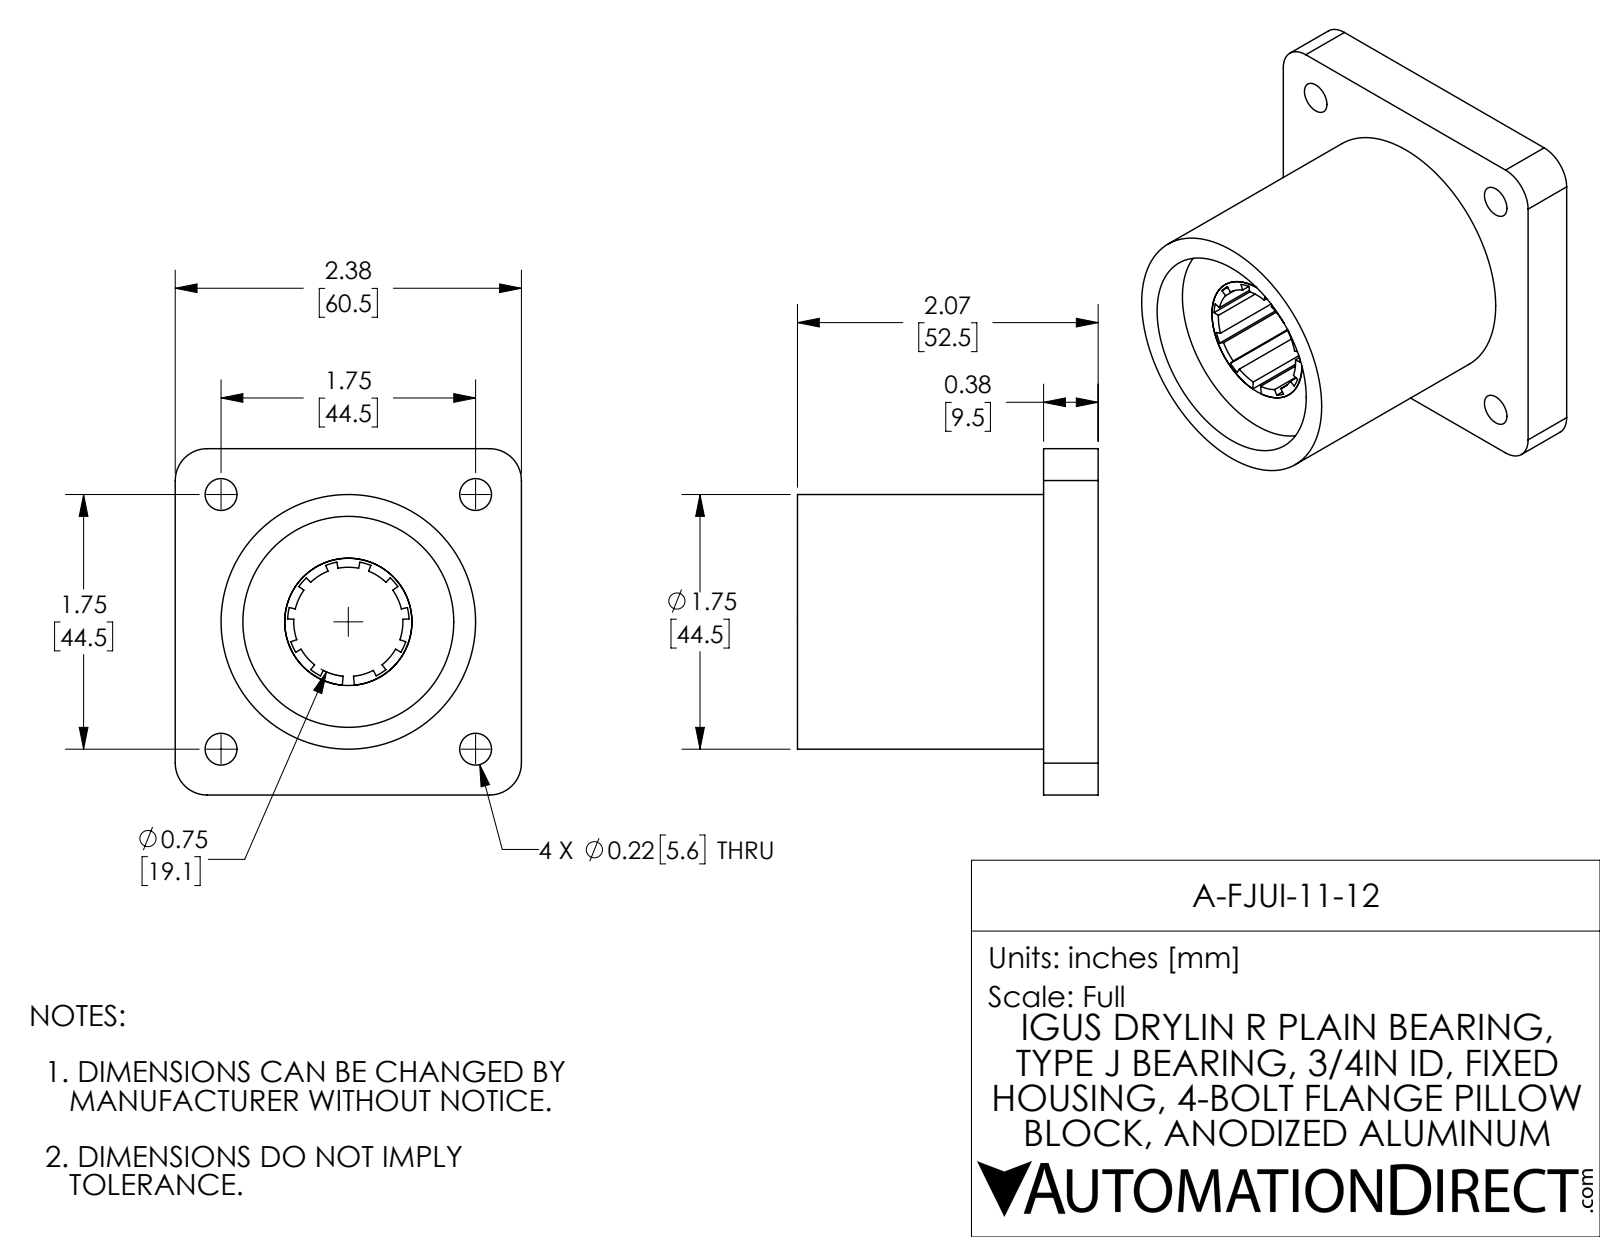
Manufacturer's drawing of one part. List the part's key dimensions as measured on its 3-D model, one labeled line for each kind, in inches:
Part name (STEP PRODUCT): A-FJUI-11-12
STEP written by: SolidWorks 2017 (AUTOMOTIVE_DESIGN)
Units: inches
Bodies: 2 solids, 135 faces (76 planar, 59 cylindrical, 0 other)
Overall size (bounding box): 2.38 × 2.38 × 2.067
Volume: 4.567 in³ · Surface area: 40.08 in²
Round holes (diameter × count): ⌀0.219 ×4, ⌀1.45 ×1
Round bosses / shafts (diameter × count): ⌀1.75 ×1, ⌀0.875 ×1, ⌀0.134 ×1
Partial cylindrical surfaces — rounded edges, fillets, slot ends (radius × count): R0.219 ×4, R0.375 ×1, R0.418 ×1, R0.469 ×1
Main face-to-face distances: 0.375, 1.821, 0.246, 2.38, 1.446, 0.129, 1.575, 2.067, 1.692, 0.94
Hole centre spacings: 1.238, 1.75, 2.476
